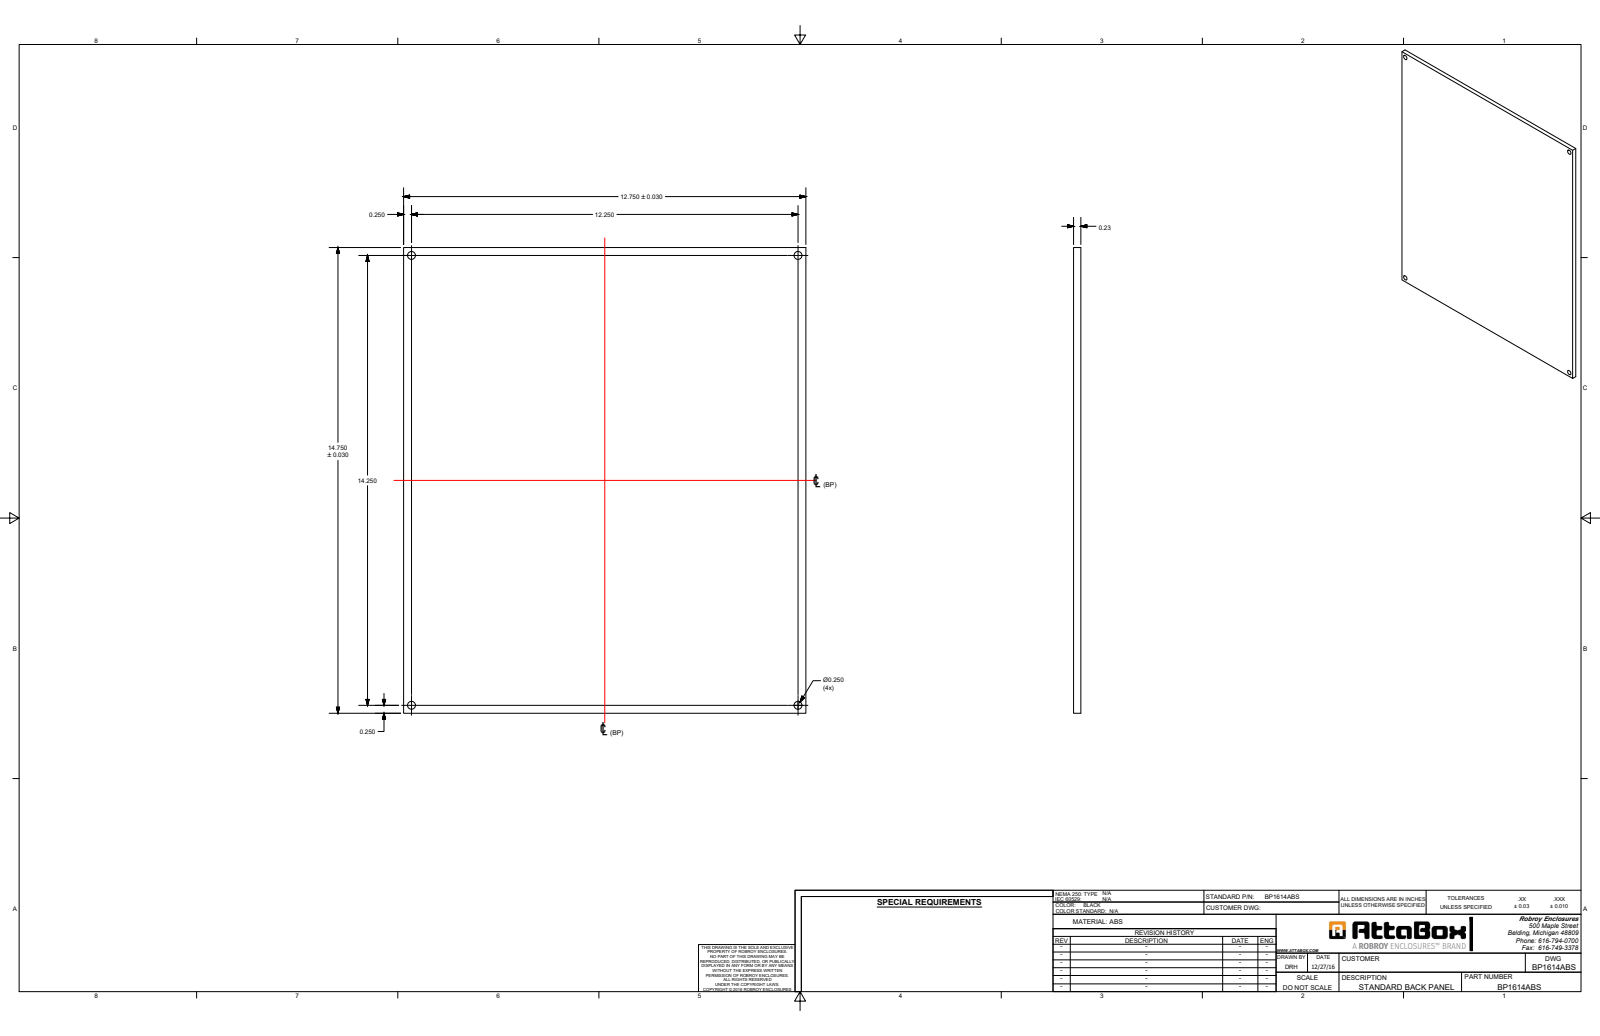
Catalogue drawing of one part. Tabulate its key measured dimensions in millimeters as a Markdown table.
| quantity | value |
| --- | --- |
| part name | BP1614ABS_Default |
| STEP written by | SolidWorks 2023 (CONFIG_CONTROL_DESIGN) |
| units | millimeters |
| bodies | 1 solid, 10 faces (6 planar, 4 cylindrical, 0 other) |
| overall size | 374.7 × 323.9 × 5.8 |
| volume | 708 100 mm³ |
| surface area | 251 000 mm² |
| round holes (diameter × count) | 6.4 × 4 |
| main face-to-face distances | 5.8, 323.9, 374.7 |
| hole center spacings | 311.2, 362, 477.3 |
